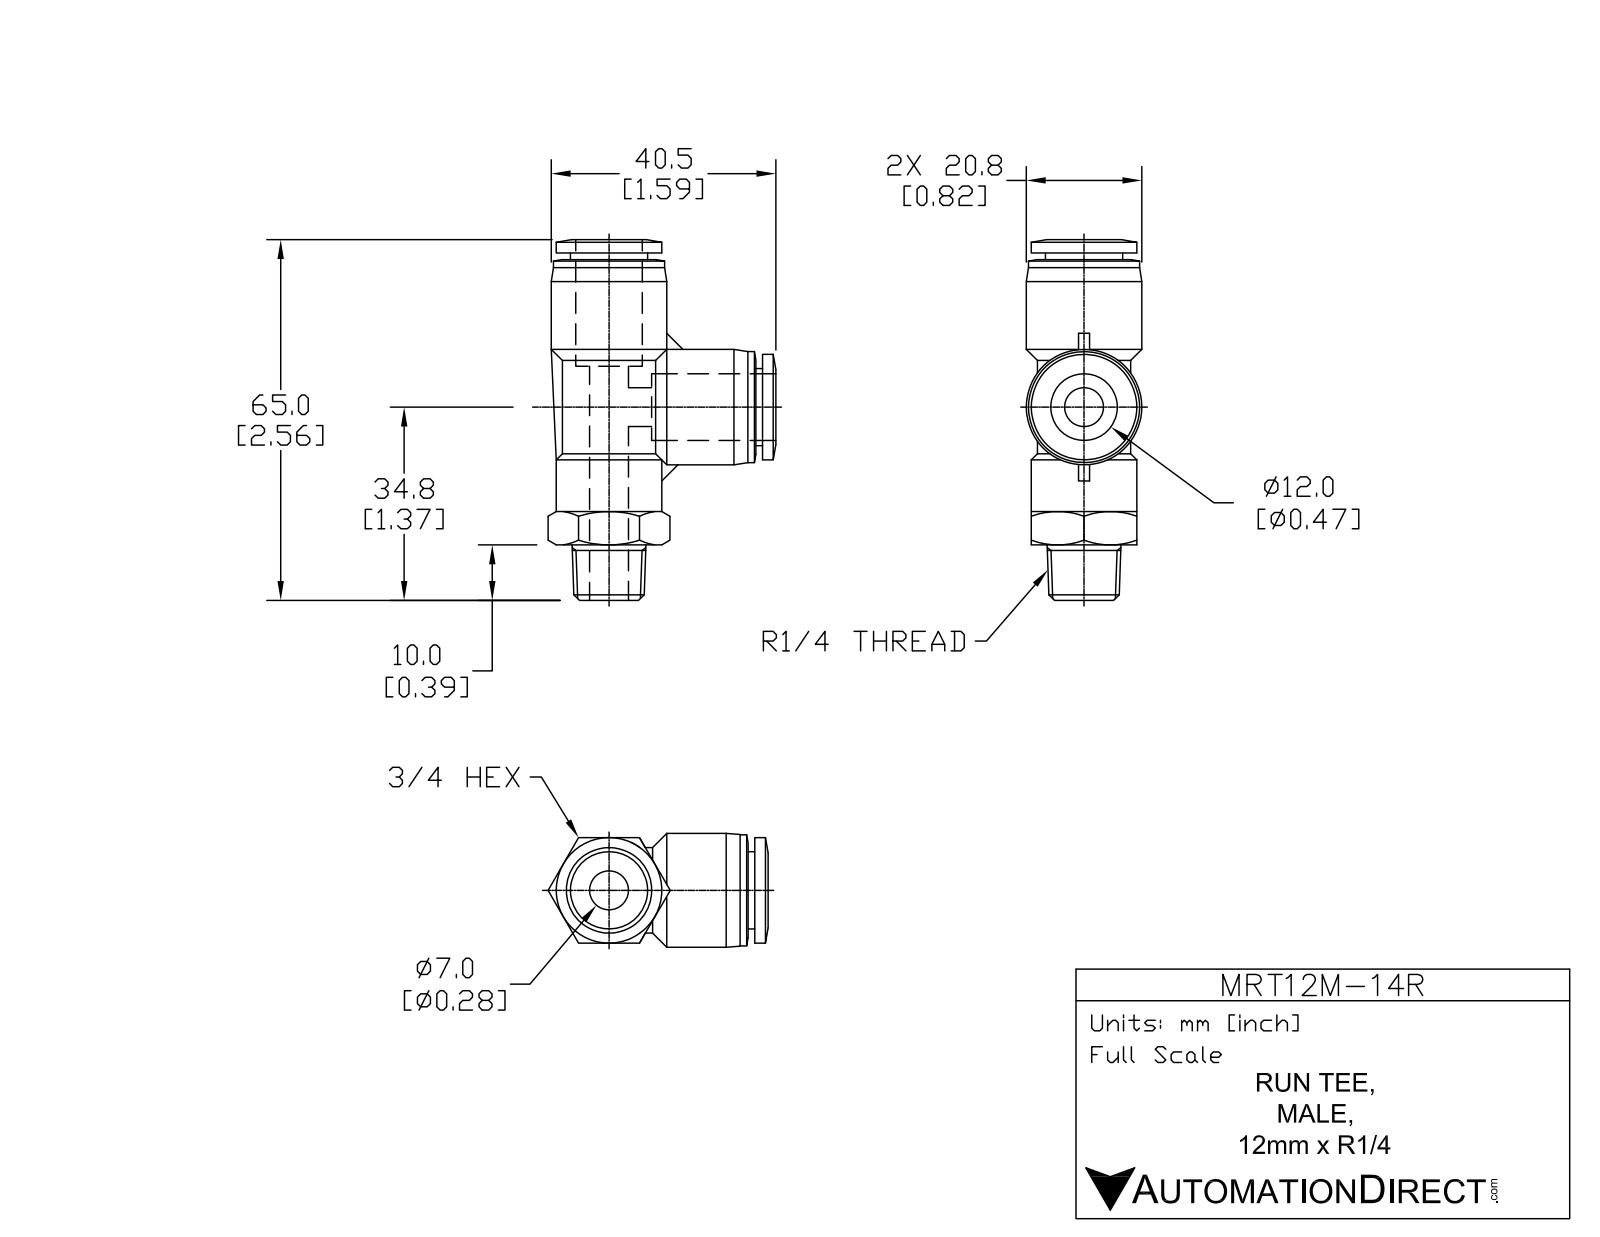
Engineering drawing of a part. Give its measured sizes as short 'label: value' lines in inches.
name: MRT12M-14R
written by: SolidWorks 2015 (AUTOMOTIVE_DESIGN)
unit: in
bodies: 1 solid, 98 faces (24 planar, 33 cylindrical, 41 other)
size: 2.561 × 1.619 × 0.819
volume: 0.941 in³; area: 14.32 in²
holes: 2× ⌀0.354, 2× ⌀0.484
bosses: 2× ⌀0.819, 2× ⌀0.787, 2× ⌀0.748, 2× ⌀0.661, 2× ⌀0.547
face distances: 0.748, 0.047, 2.073, 0.76, 0.807, 0.335, 0.413, 2.026, 1.266, 0.079
